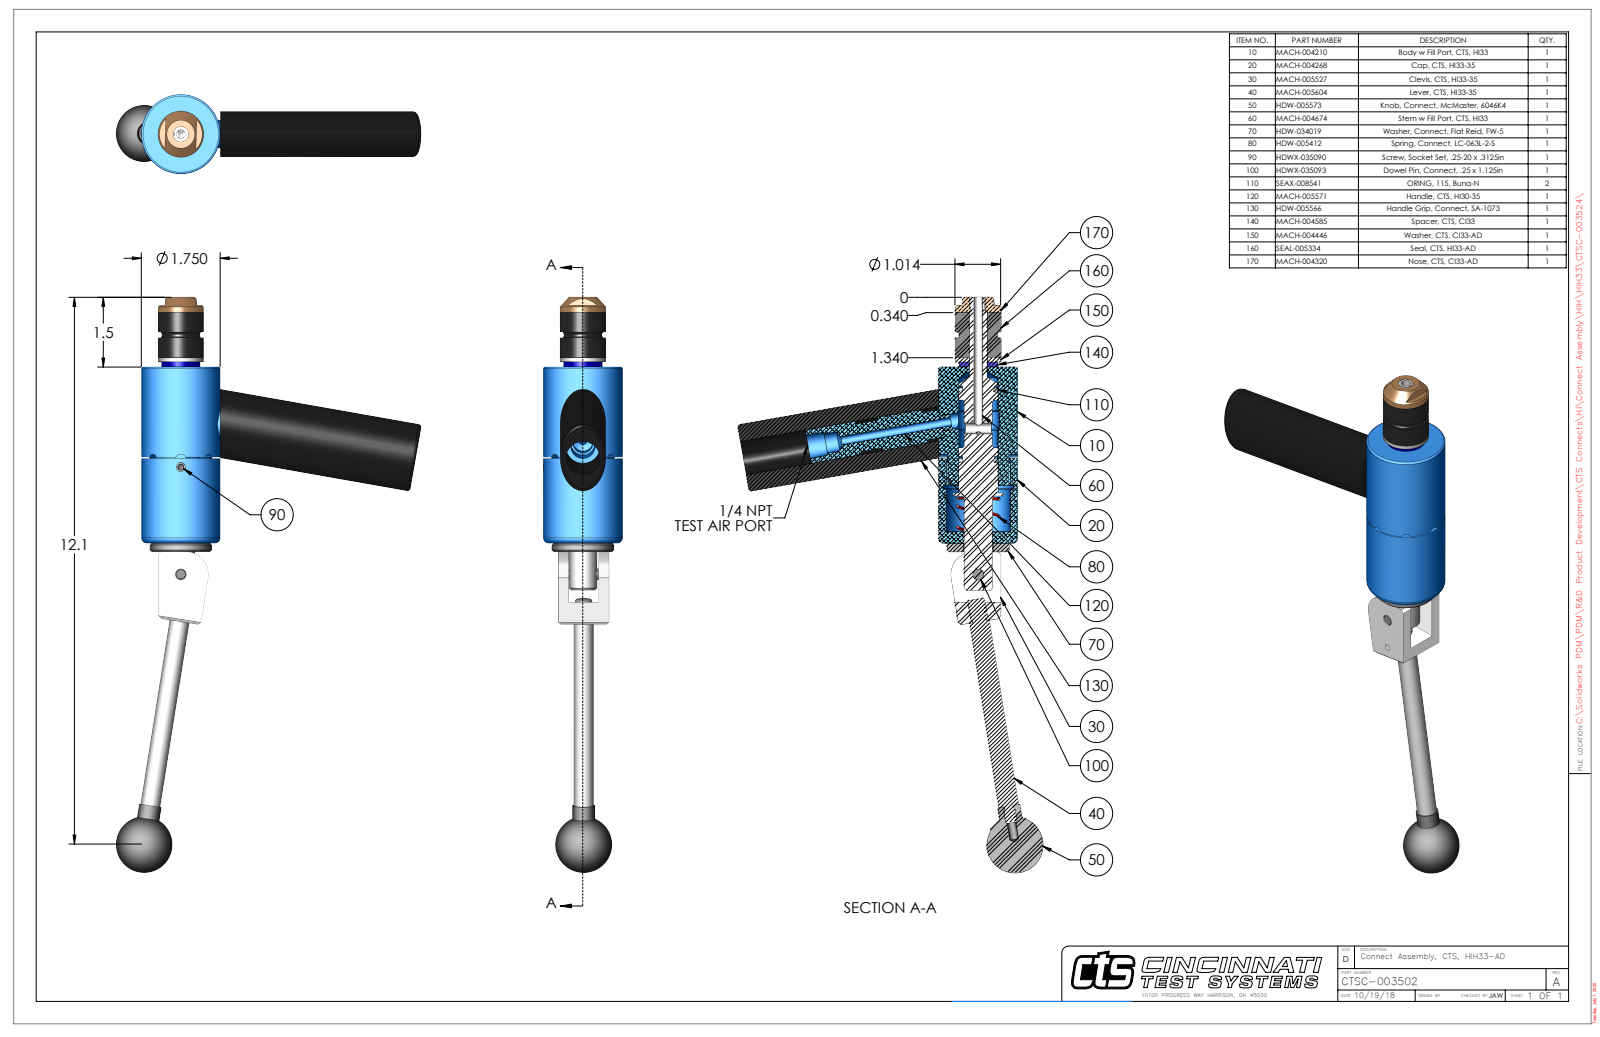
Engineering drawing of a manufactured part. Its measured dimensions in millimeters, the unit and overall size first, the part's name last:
Units: millimetres
Overall size (bounding box): 323.9 × 171.8 × 44.5
Round holes (diameter × count): ⌀5.1 ×2, ⌀8 ×2, ⌀3.8 ×1, ⌀4.7 ×1, ⌀5.2 ×1, ⌀6.3 ×1, ⌀6.4 ×1, ⌀6.4 ×1, ⌀9.9 ×1, ⌀10.1 ×1, ⌀10.2 ×1, ⌀11.1 ×1
Round bosses / shafts (diameter × count): ⌀9.5 ×2, ⌀7.9 ×2, ⌀6.4 ×2, ⌀44.5 ×1, ⌀35.1 ×1, ⌀25.8 ×1, ⌀21.8 ×1, ⌀19.1 ×1
Partial cylindrical surfaces — rounded edges, fillets, slot ends (radius × count): R3.2 ×4, R0.7 ×2, R3.7 ×1, R8.4 ×1, R12.7 ×1, R17.7 ×1, R21.4 ×1
Main face-to-face distances: 99.2, 28.4, 30.7, 129.9, 25.4, 5.3, 104.5, 134.7, 109.3, 104
Hole centre spacings: 18.8, 60.4, 79.1
Volume: 293 000 mm³ · Surface area: 72 450 mm²
Bodies: 11 solids, 287 faces (93 planar, 125 cylindrical, 69 other)
Part name (STEP PRODUCT): CTSC-003524
STEP written by: SolidWorks 2023 (AUTOMOTIVE_DESIGN)
